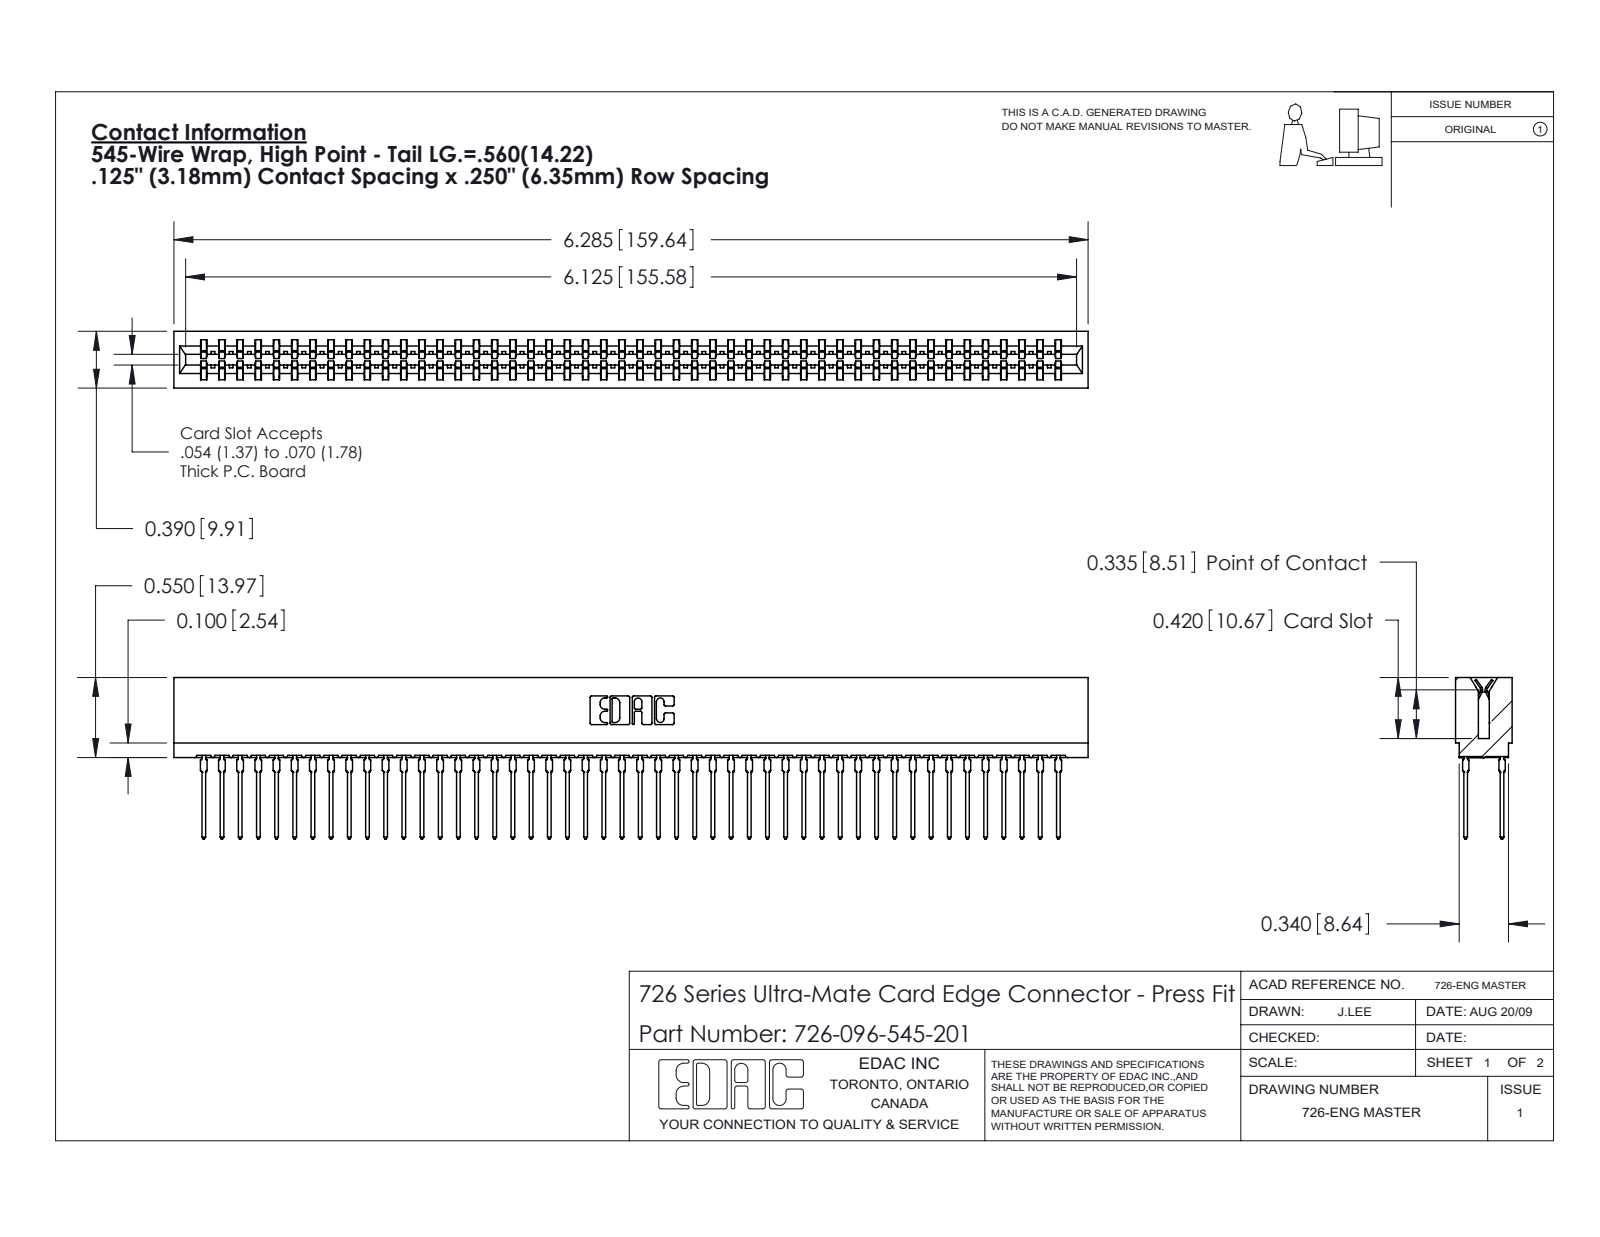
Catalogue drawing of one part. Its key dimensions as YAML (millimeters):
part_name: "726 Part_.515 Slot Depth - 01; 746-292-001_545; 726-096-545-201"
step_written_by: "SolidWorks 2020 (CONFIG_CONTROL_DESIGN)"
units: millimeters
bodies: {solids: 97, faces: 8689, planar: 4471, cylindrical: 1722, other: 2496}
overall_size: [159.6, 28.2, 9.9]
volume: 15000
surface_area: 26620
partial_cylinders:
  - {radius: 0.5, count: 192}
  - {radius: 0.4, count: 49}
  - {radius: 0.3, count: 22}
  - {radius: 0.1, count: 8}
  - {radius: 0.3, count: 8}
  - {radius: 0.2, count: 6}
  - {radius: 0.8, count: 6}
  - {radius: 0.7, count: 3}
face_to_face_distances: [1.4, 8.5, 0.6, 7.8, 9.9, 6.4, 2.1, 7, 9.3, 0.8]
